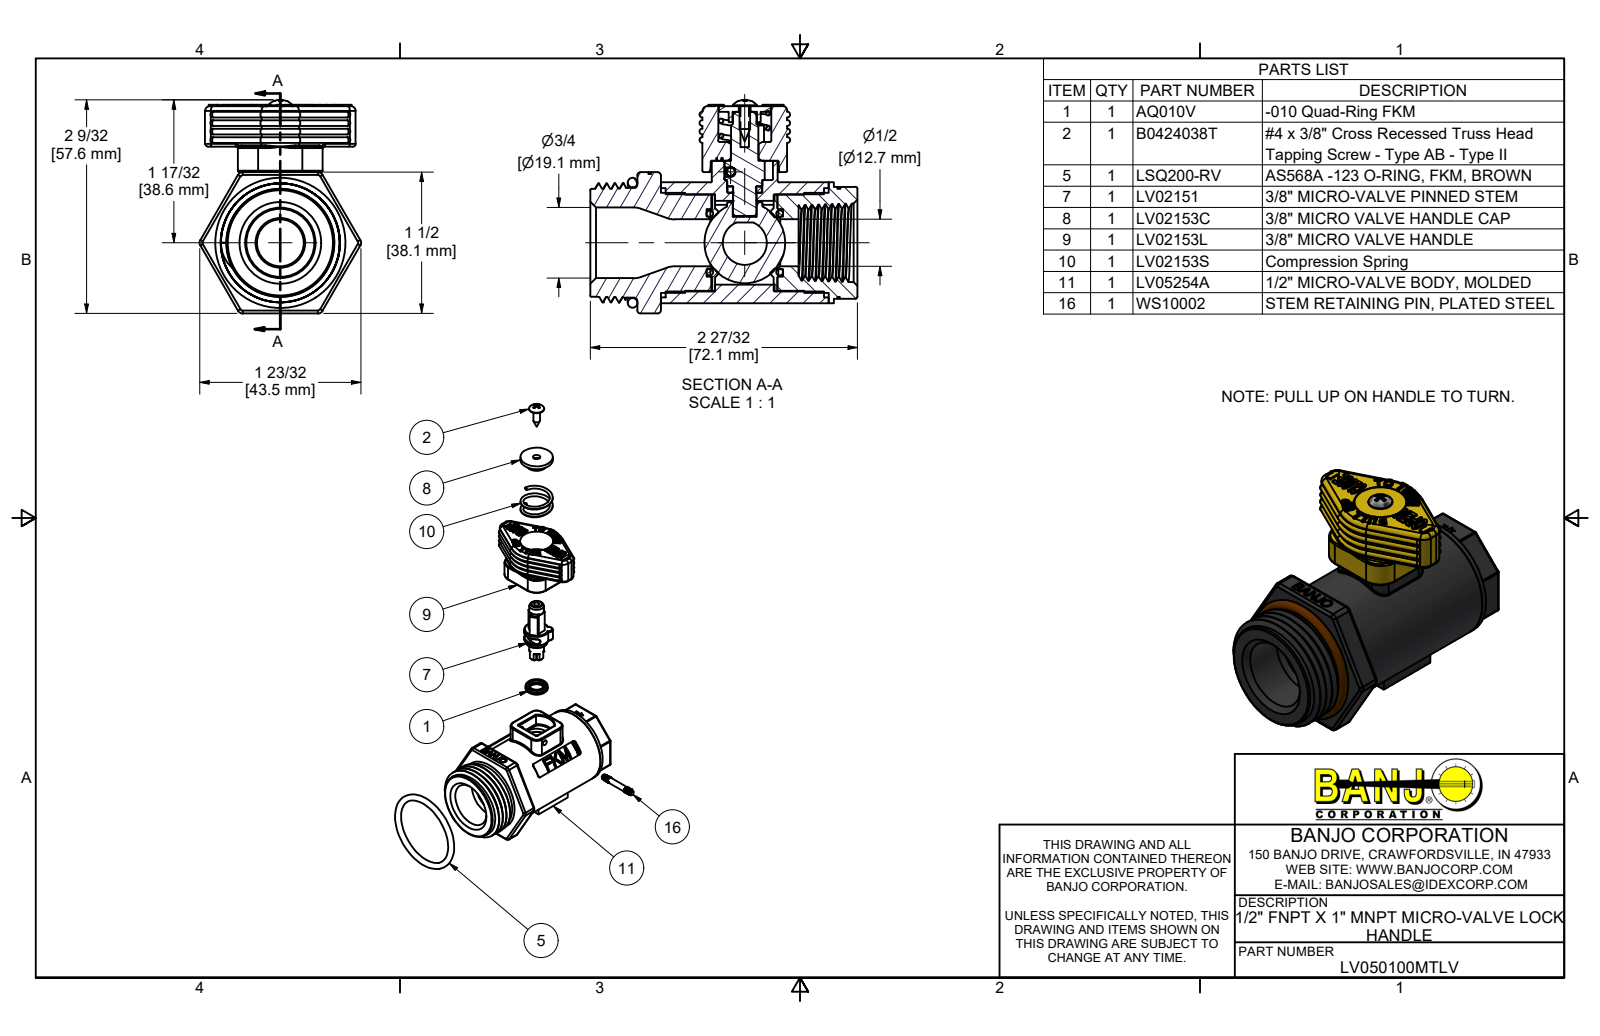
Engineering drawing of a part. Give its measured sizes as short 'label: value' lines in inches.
name: LV050100MTLV; LV05254A; LV05256A1; LV05256A (+8 more)
written by: Autodesk Inventor 2022 (AUTOMOTIVE_DESIGN)
unit: in
bodies: 19 solids, 3494 faces (2309 planar, 278 cylindrical, 907 other)
size: 2.837 × 2.269 × 1.714
volume: 3.396 in³; area: 56.27 in²
holes: 1× ⌀0.089, 1× ⌀0.093, 1× ⌀0.125, 1× ⌀0.181, 1× ⌀0.251, 1× ⌀0.257, 1× ⌀0.26, 1× ⌀0.366, 1× ⌀0.376, 1× ⌀0.47, 1× ⌀0.5, 1× ⌀0.541
bosses: 1× ⌀1.285, 1× ⌀1.165, 1× ⌀1.064, 1× ⌀1.062, 1× ⌀1.024, 1× ⌀1.02, 1× ⌀0.558, 1× ⌀0.552
rounds: 56× R0.03, 36× R0.015, 16× R0.01, 16× R0.02, 10× R0.06, 8× R0.05, 4× R0.109, 4× R0.125
face distances: 0.05, 1.237, 0.545, 1.207, 0.575, 1.247, 0.662, 0.25, 0.02, 0.535
hole spacings: 0.39, 0.641, 0.769
